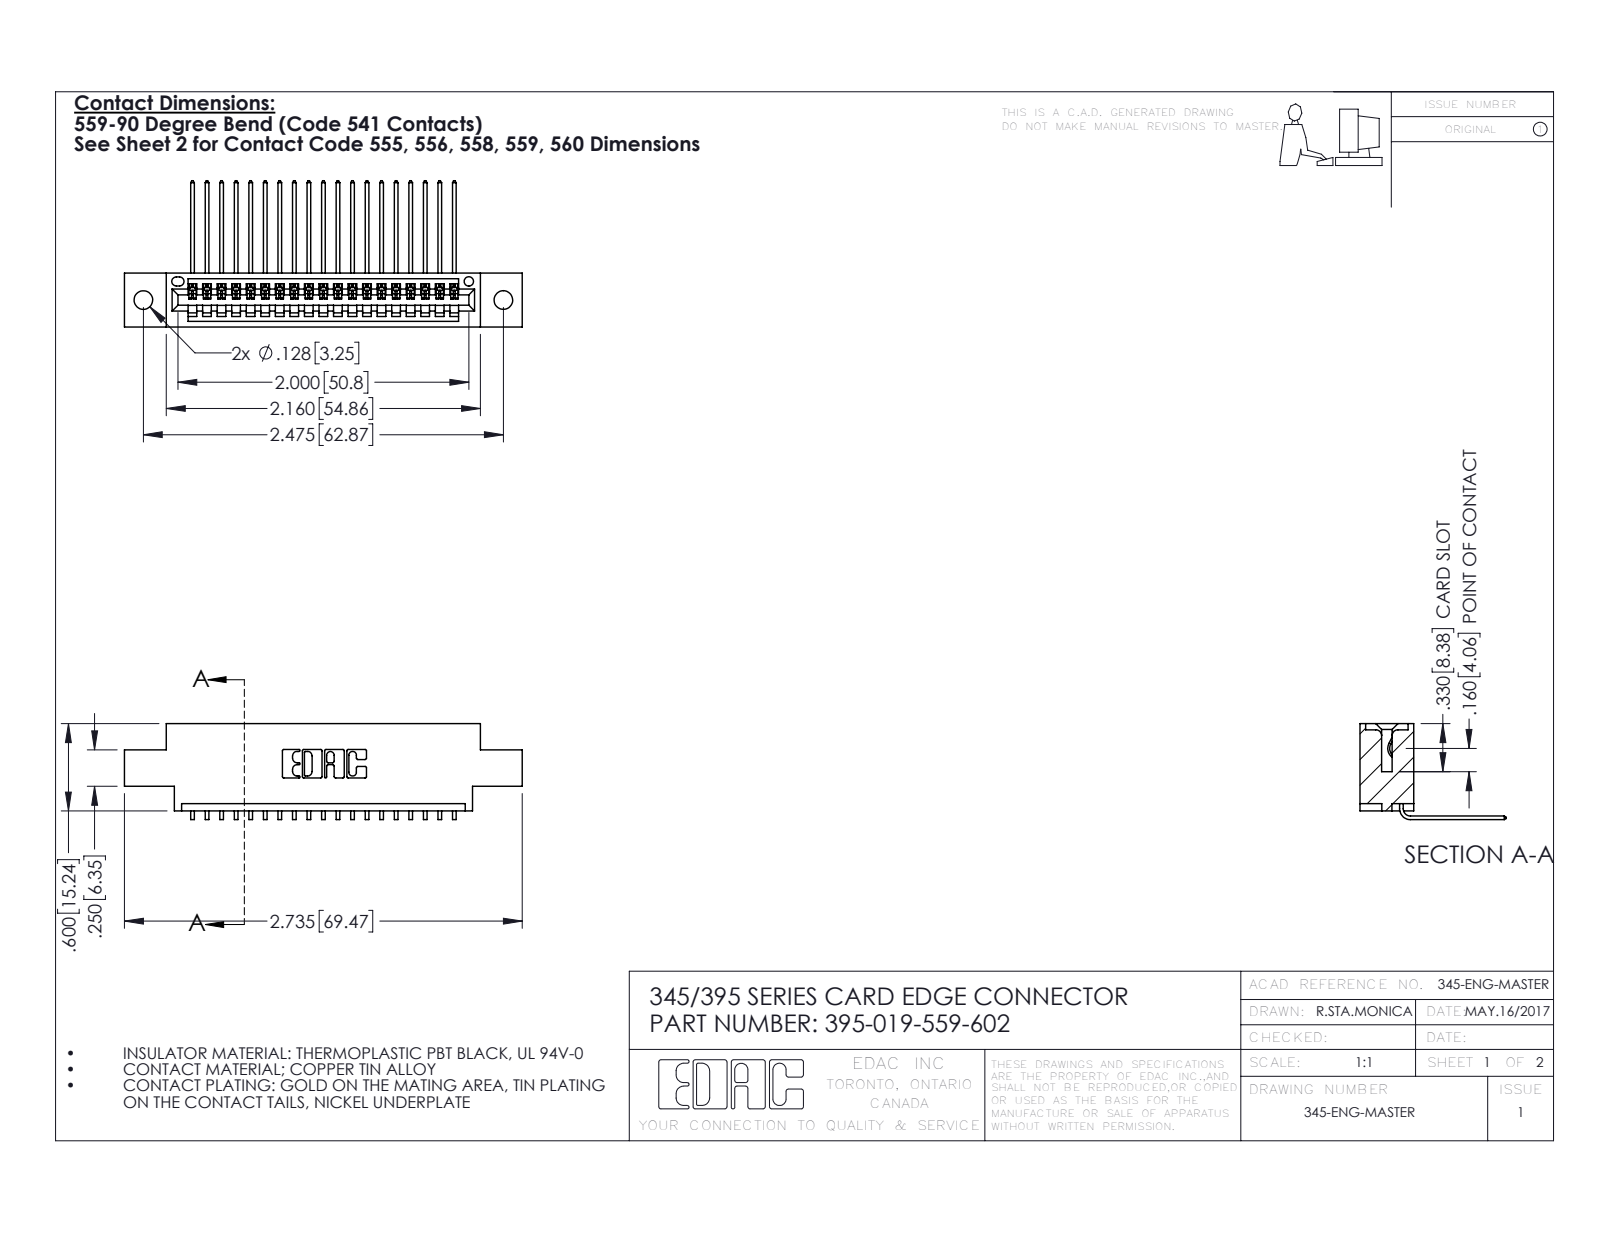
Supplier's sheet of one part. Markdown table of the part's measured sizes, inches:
| quantity | value |
| --- | --- |
| part name | 345-292-001_558 559 Tail - 1; 395-019-559-602; 345 Part_0.170 Offset - 0.128 Dia |
| STEP written by | SolidWorks 2016 (CONFIG_CONTROL_DESIGN) |
| units | inches |
| bodies | 20 solids, 1270 faces (882 planar, 388 cylindrical, 0 other) |
| overall size | 2.735 × 1.005 × 0.659 |
| volume | 0.386 in³ |
| surface area | 12.89 in² |
| round holes (diameter × count) | 0.128 × 2, 0.064 × 1 |
| partial cylindrical surfaces (radius × count) | 0.006 × 38, 0.01 × 22, 0.007 × 6, 0.031 × 6, 0.026 × 3, 0.031 × 2, 0.04 × 2, 0.014 × 1 |
| main face-to-face distances | 0.37, 0.072, 0.298, 0.2, 0.098, 0.272, 0.025, 0.225, 0.1, 0.15 |
| hole center spacings | 0.27, 2.241, 2.475 |
